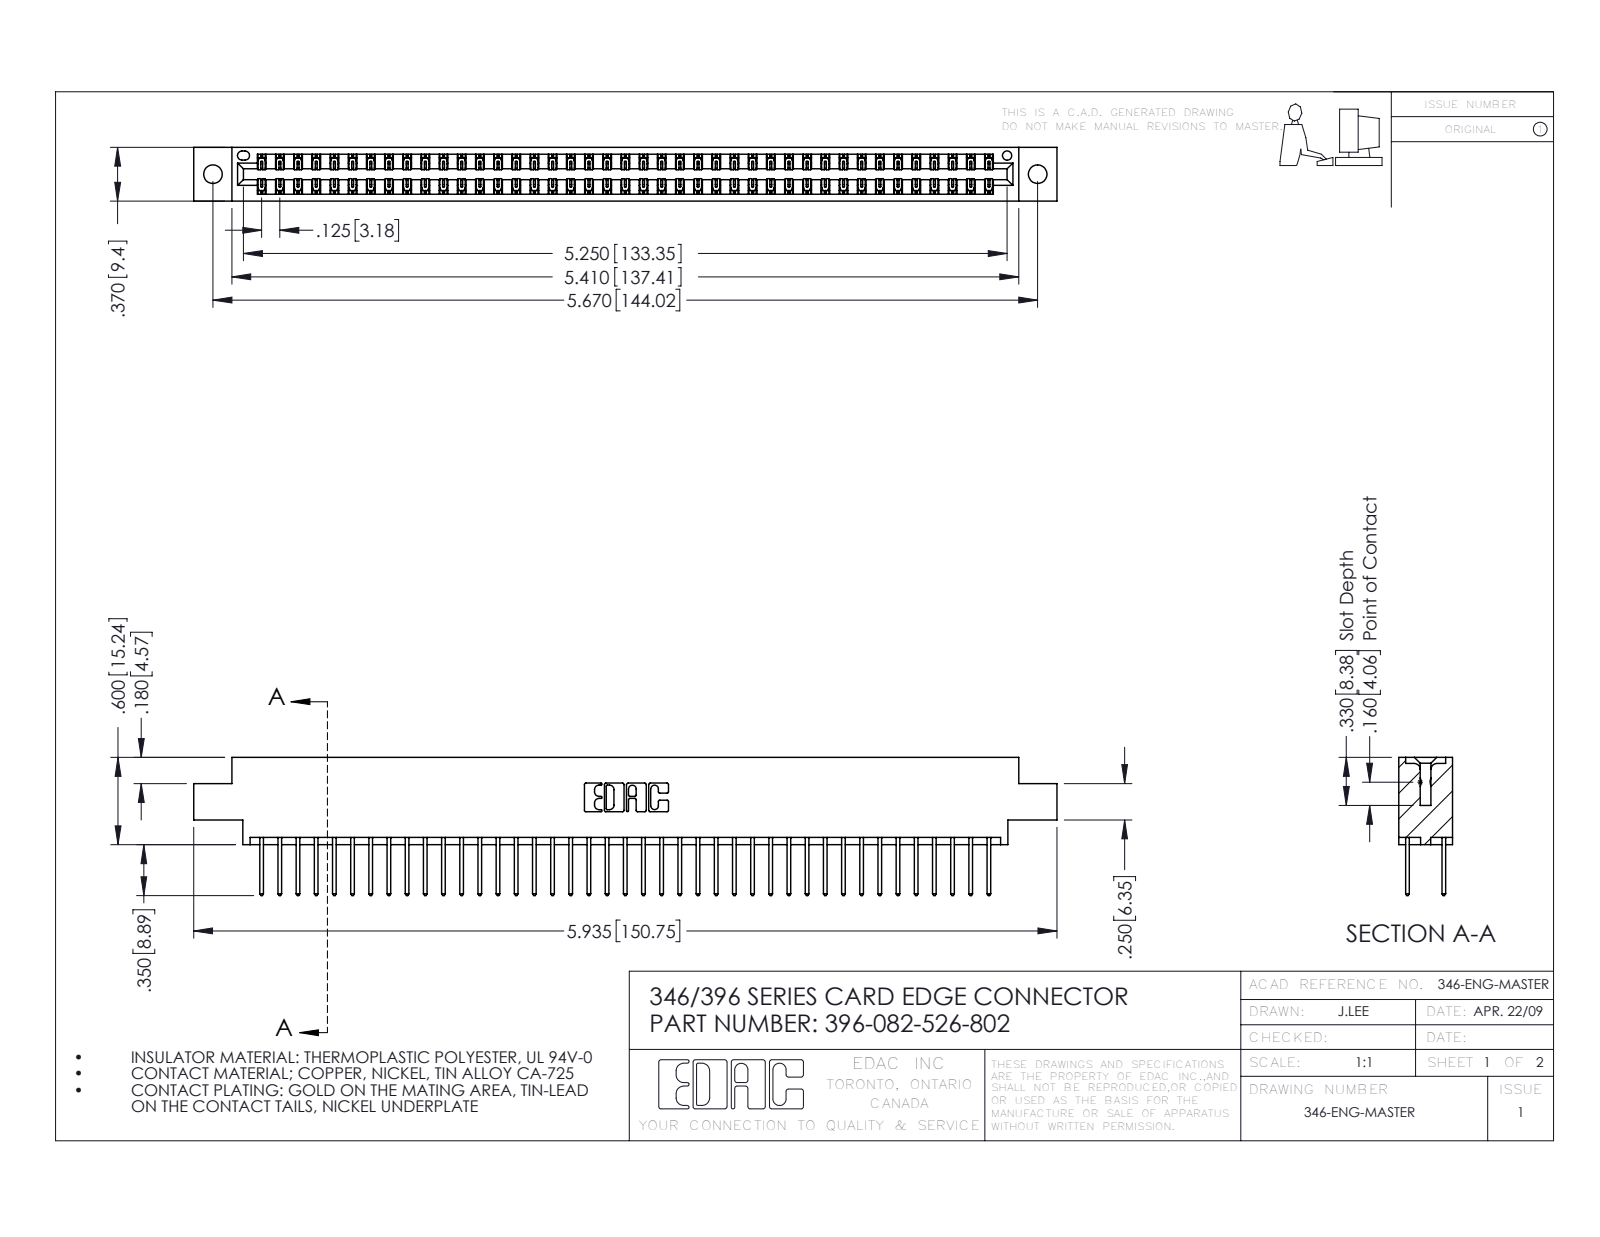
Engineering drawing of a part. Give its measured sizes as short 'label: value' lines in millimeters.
name: 396-082-526-802; 346 Part_0.170 Offset - 0.128 Dia; 345-292-001_345-293-126
written by: SolidWorks 2016 (CONFIG_CONTROL_DESIGN)
unit: mm
bodies: 83 solids, 4390 faces (2950 planar, 1440 cylindrical, 0 other)
size: 150.7 × 24.1 × 9.4
volume: 14 600 mm³; area: 20 610 mm²
holes: 2× ⌀3.3, 1× ⌀1.6
rounds: 123× R0.2, 82× R0.3, 22× R0.3, 6× R0.2, 6× R0.8, 3× R0.7, 2× R0.4, 2× R0.6
face distances: 1.2, 8.2, 6.4, 9.4, 1.8, 7.6, 0.6, 7, 3.8, 5.6
hole spacings: 6.2, 138.7, 144
